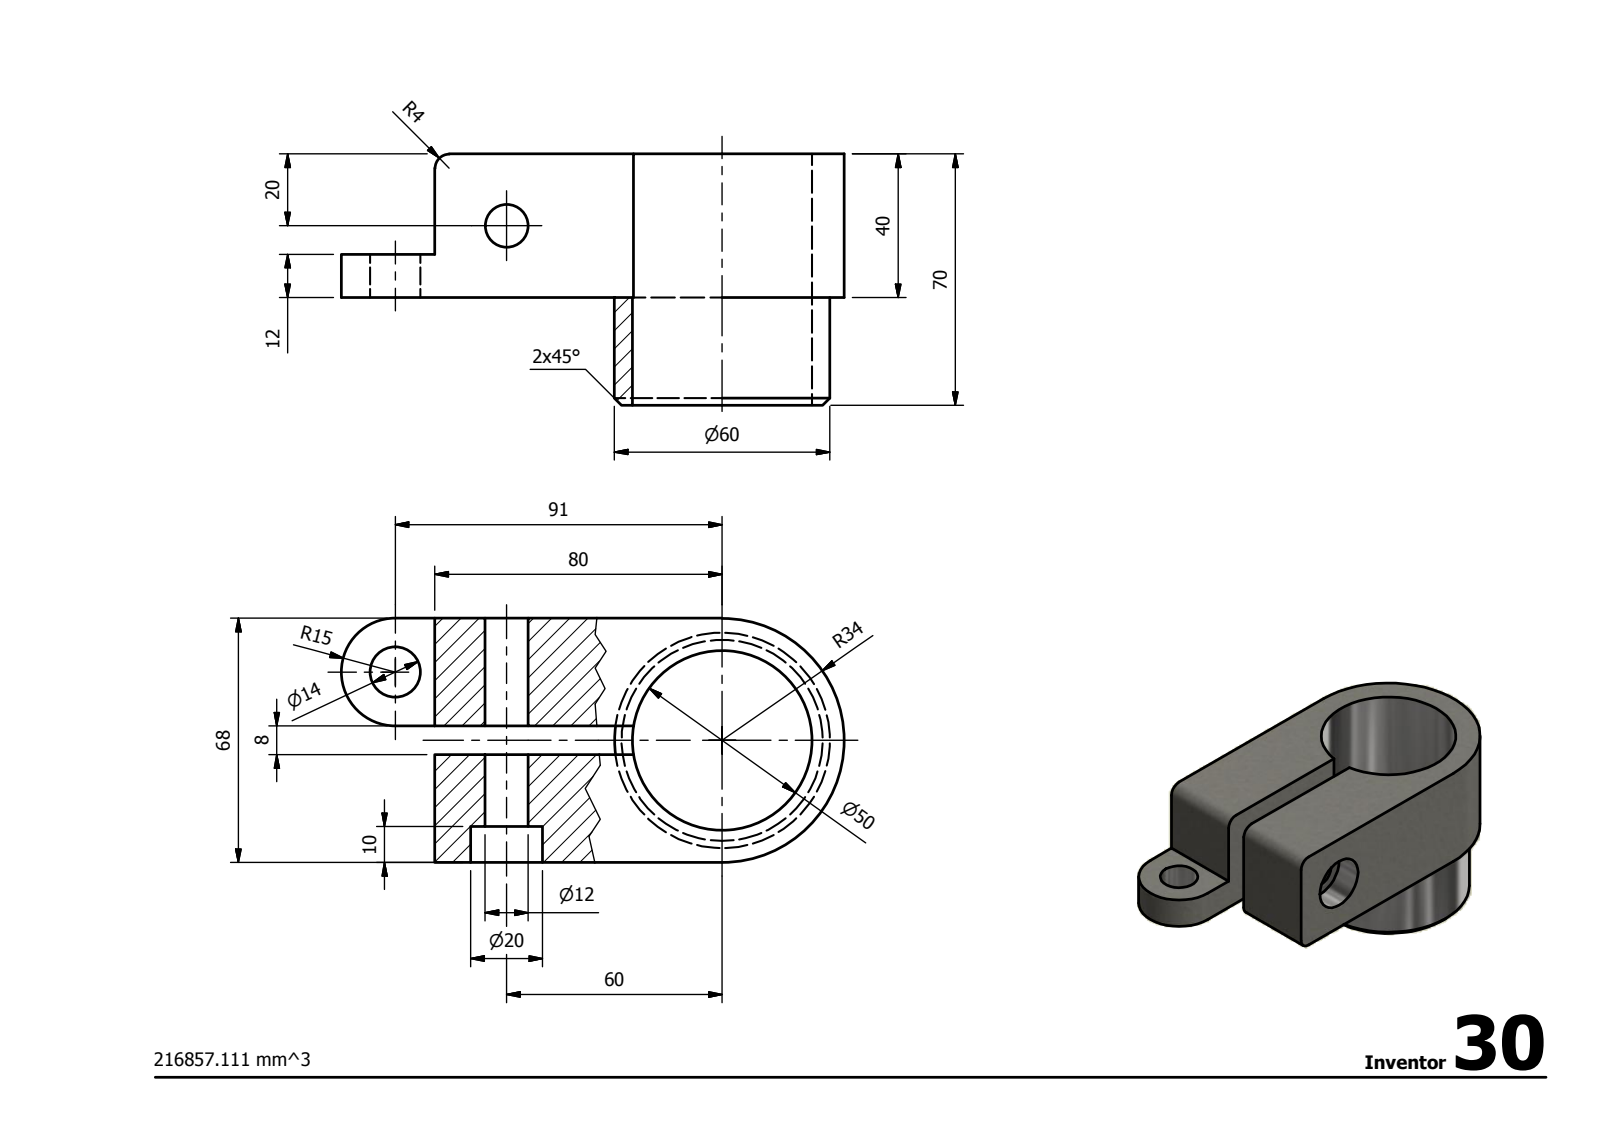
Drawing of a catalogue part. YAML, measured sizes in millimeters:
step_written_by: "Autodesk Inventor 2014 (AUTOMOTIVE_DESIGN)"
units: millimeters
bodies: {solids: 1, faces: 24, planar: 12, cylindrical: 11, other: 1}
overall_size: [140, 70, 68]
volume: 216857
surface_area: 47327
round_holes:
  - {diameter: 12, count: 1}
  - {diameter: 14, count: 1}
  - {diameter: 20, count: 1}
  - {diameter: 50, count: 1}
round_bosses_or_shafts:
  - {diameter: 60, count: 1}
partial_cylinders:
  - {radius: 4, count: 2}
  - {radius: 15, count: 1}
  - {radius: 34, count: 1}
face_to_face_distances: [30, 40, 38, 68, 8, 28, 12, 42, 70, 58]
hole_center_spacings: [92.96]
